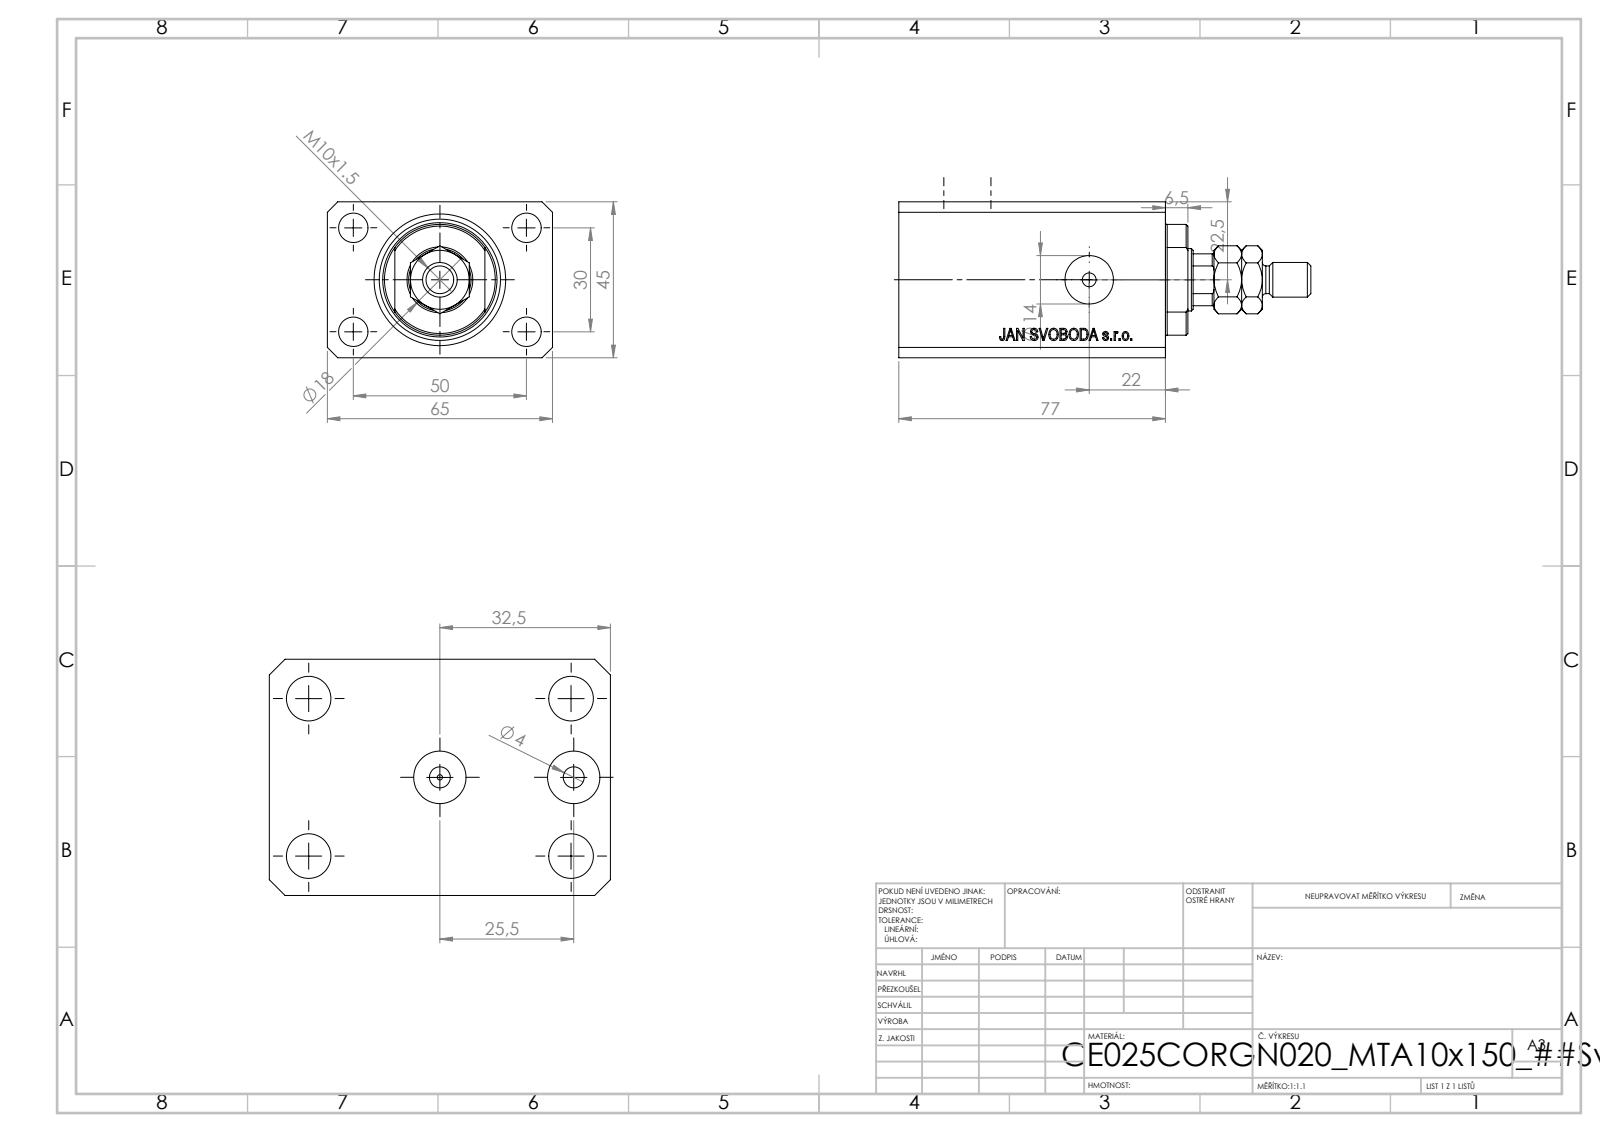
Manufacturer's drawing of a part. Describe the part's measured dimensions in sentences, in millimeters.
The part is named "V250CE_C_VCP; V250CE_VC_C; V250CE_C_Body; MTA". Its 3-D file was written by "SolidWorks 2019 (CONFIG_CONTROL_DESIGN)". It is 4 solids with 921 faces: 443 planar, 54 cylindrical and 424 other. Overall it measures 119 by 65 by 45 millimeters. Its volume is 207 926 cubic millimeters and its surface area 52 492 square millimeters. Round holes: 5 of diameter 8.5, 4 of diameter 4, 2 of diameter 10, 2 of diameter 14, 1 of diameter 1.25, 1 of diameter 18, 1 of diameter 25, 1 of diameter 38. Round bosses or shafts: 1 of diameter 8. Partial cylindrical surfaces (rounded edges, fillets, slot ends): 1 of radius 8.5, 1 of radius 16. The main face-to-face distances are 45, 65, 14, 77, 63, 6.9, 56.1, 70.1, 73.52, 28. The hole center spacings are 29.15, 15.01, 30, 50, 52.68, 58.31, 25.5, 33.
